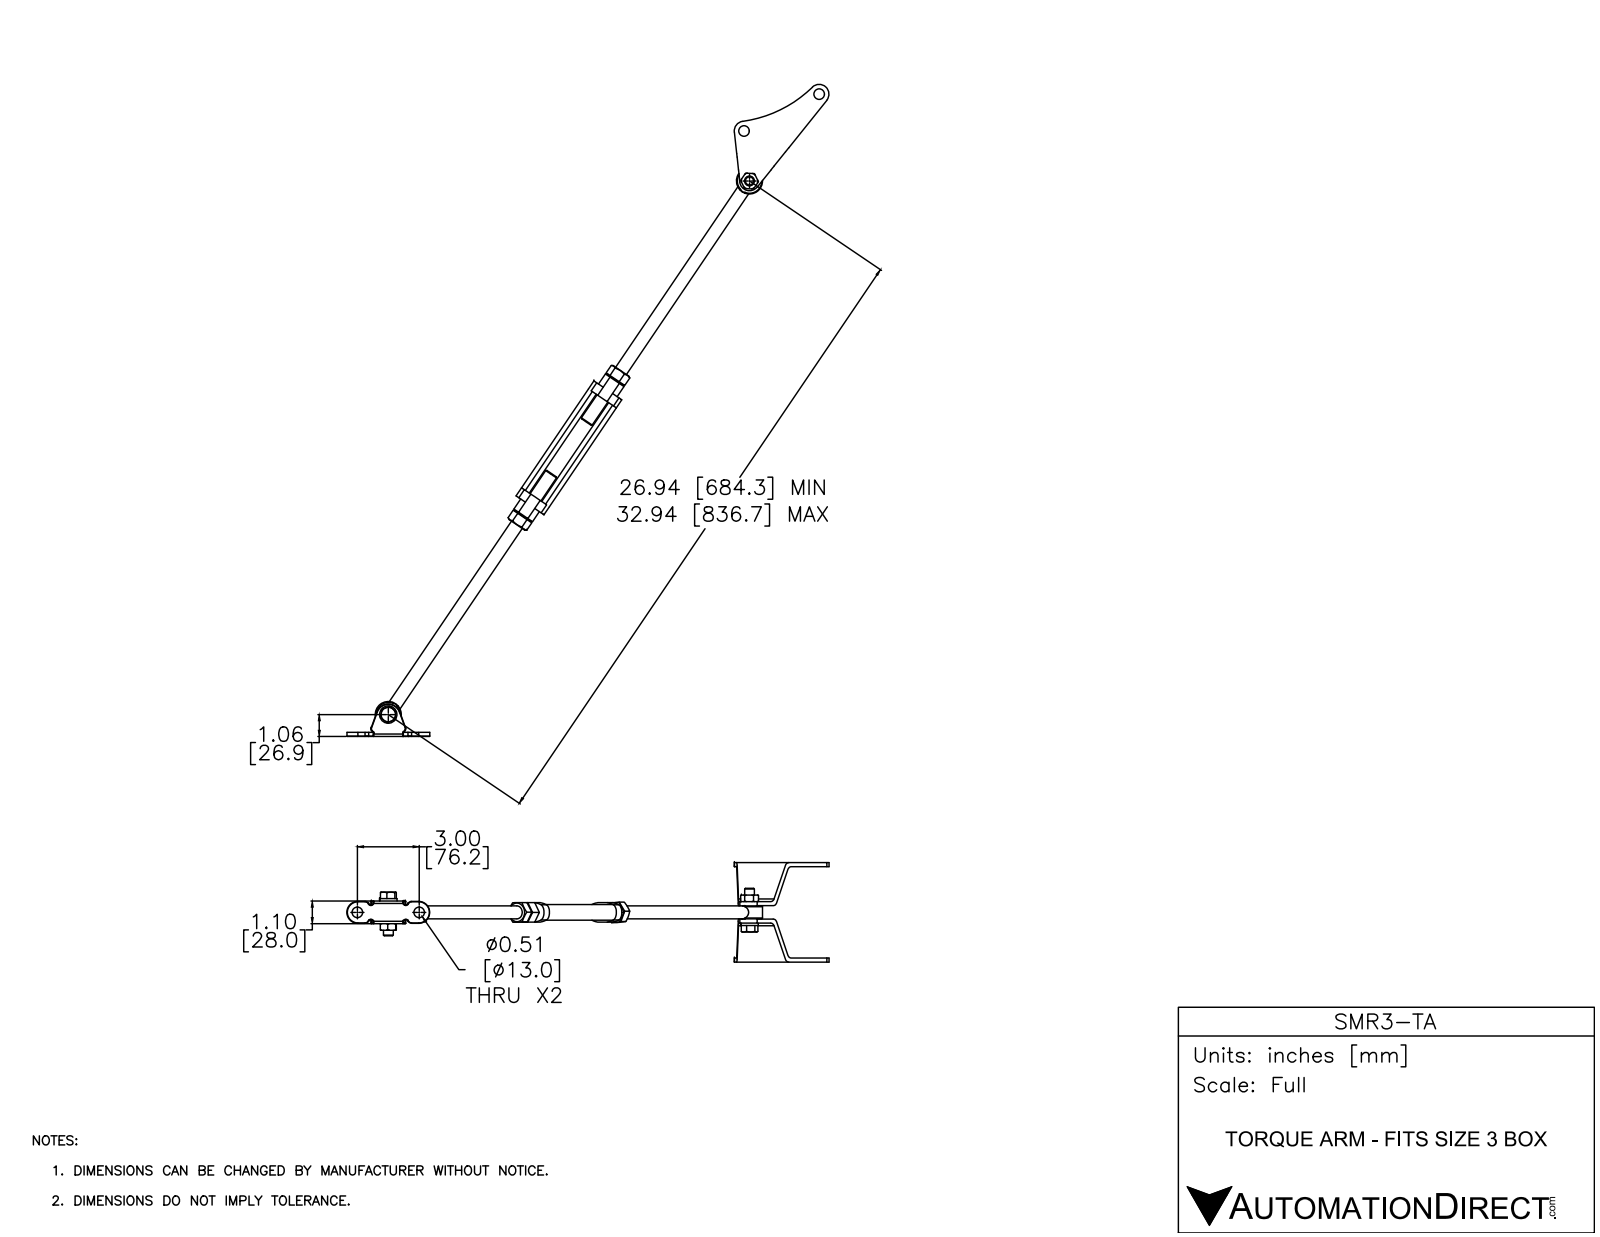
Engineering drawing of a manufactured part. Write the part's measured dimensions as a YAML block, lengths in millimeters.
part_name: "SMR3-TA_5; SMR3-TA_1; SMR3-TARM; SMR3-TA_2 (+2 more)"
step_written_by: "SolidWorks 2017 (AUTOMOTIVE_DESIGN)"
units: millimeters
bodies: {solids: 15, faces: 410, planar: 152, cylindrical: 128, other: 130}
overall_size: [803, 593.9, 122.5]
volume: 365900
surface_area: 129700
round_holes:
  - {diameter: 13, count: 5}
  - {diameter: 12, count: 2}
  - {diameter: 12.2, count: 2}
  - {diameter: 12.9, count: 2}
  - {diameter: 16, count: 2}
  - {diameter: 14, count: 1}
  - {diameter: 17.2, count: 1}
round_bosses_or_shafts:
  - {diameter: 32, count: 2}
  - {diameter: 22.3, count: 2}
  - {diameter: 21.5, count: 2}
  - {diameter: 16, count: 2}
  - {diameter: 17, count: 1}
partial_cylinders:
  - {radius: 0.5, count: 22}
  - {radius: 5, count: 12}
  - {radius: 3, count: 8}
  - {radius: 12, count: 3}
  - {radius: 1, count: 2}
  - {radius: 13.5, count: 2}
  - {radius: 15, count: 1}
  - {radius: 155, count: 1}
face_to_face_distances: [5, 117.5, 122.5, 47.2, 70.3, 112.5, 48, 69.5, 0.8, 22.3]
hole_center_spacings: [62, 76.2, 103.1, 137.2, 793.6, 841.8, 930.4]
